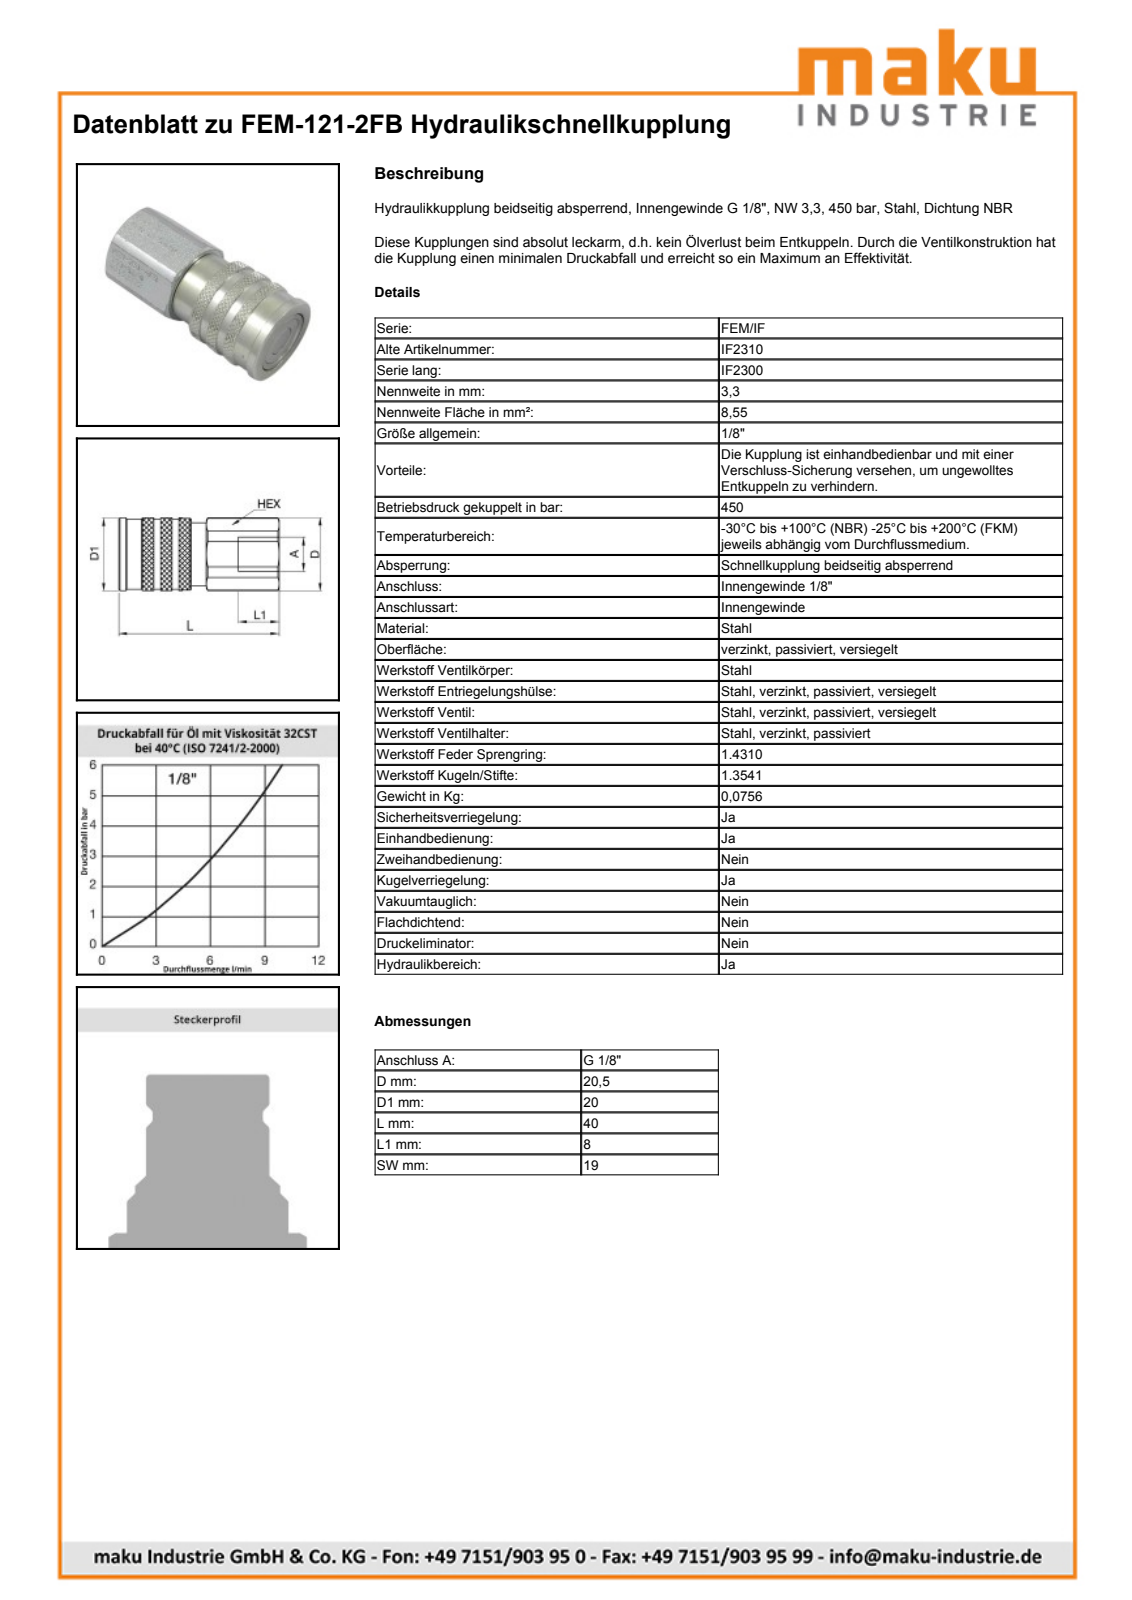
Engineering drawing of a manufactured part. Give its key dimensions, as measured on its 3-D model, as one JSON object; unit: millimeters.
{"part_name": "FEM-121-2FB", "step_written_by": "SolidWorks 2009 (AUTOMOTIVE_DESIGN)", "units": "millimeters", "bodies": {"solids": 1, "faces": 115, "planar": 30, "cylindrical": 44, "other": 41}, "overall_size": [40.4, 20.5, 20], "volume_mm3": 11558, "surface_area_mm2": 4002, "round_holes": [[2.4, 1], [7.65, 1], [8.57, 1], [11.7, 1], [15.3, 1], [17.6, 1]], "round_bosses_or_shafts": [[20, 1], [19.4, 1], [17.5, 1], [15.2, 1], [11.65, 1], [7.55, 1]], "partial_cylinders_radius": [[0.5, 2], [10.25, 1]], "face_to_face_distances": [19, 40.4, 10.67, 29.73, 4.2, 39.87, 29.2, 0.53, 0.5, 20]}
